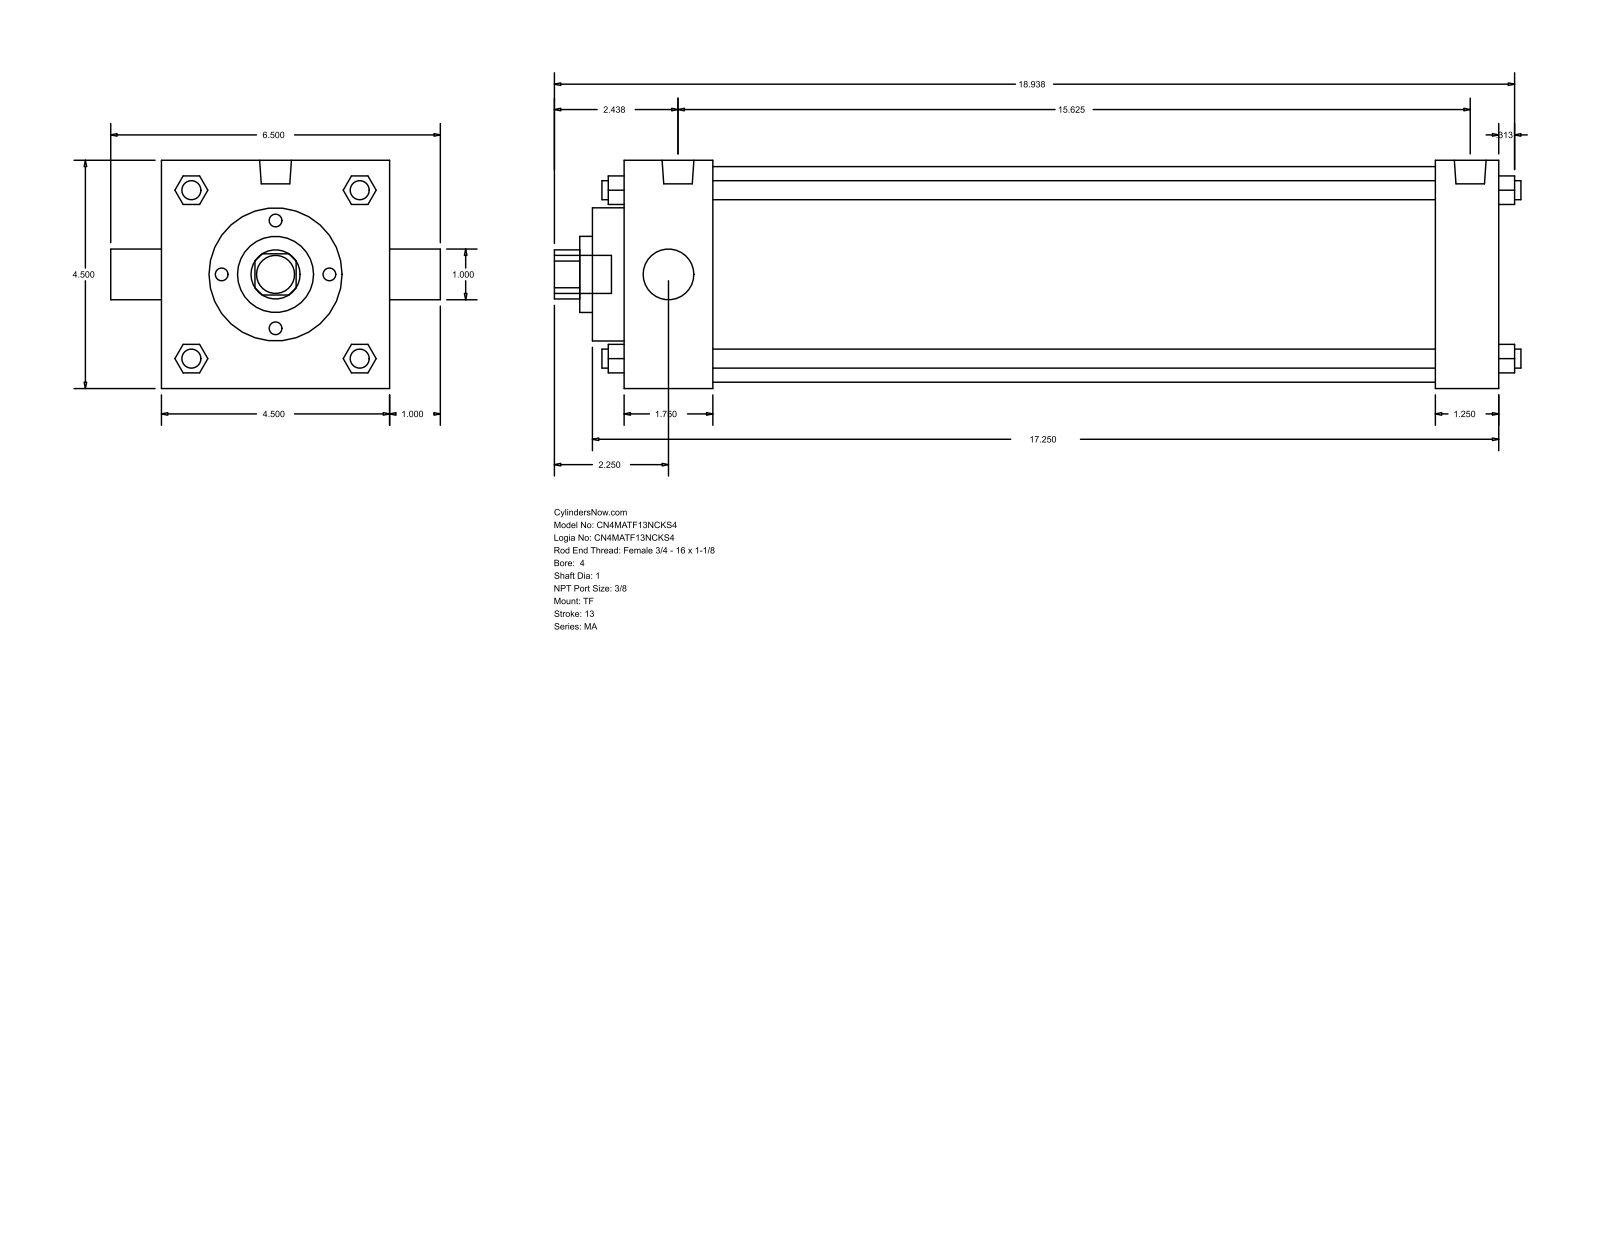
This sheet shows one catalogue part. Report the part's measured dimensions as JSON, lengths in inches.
{"part_name": "MA_TF__0400_1", "step_written_by": "GSSL Pune (CONFIG_CONTROL_DESIGN)", "units": "inches", "bodies": {"solids": 0, "faces": 122, "planar": 93, "cylindrical": 29, "other": 0}, "overall_size": [19.063, 6.5, 4.5], "round_holes": [[1, 2], [1.5, 1], [2.625, 1], [4.25, 1]], "round_bosses_or_shafts": [[0.375, 4], [0.437, 3], [0.627, 2], [0.75, 1]], "partial_cylinders_radius": [[0.484, 1]], "face_to_face_distances": [4.5, 17.25, 16, 1.25, 1.75, 14.25, 15.5, 17.875, 0.625, 2.375]}
